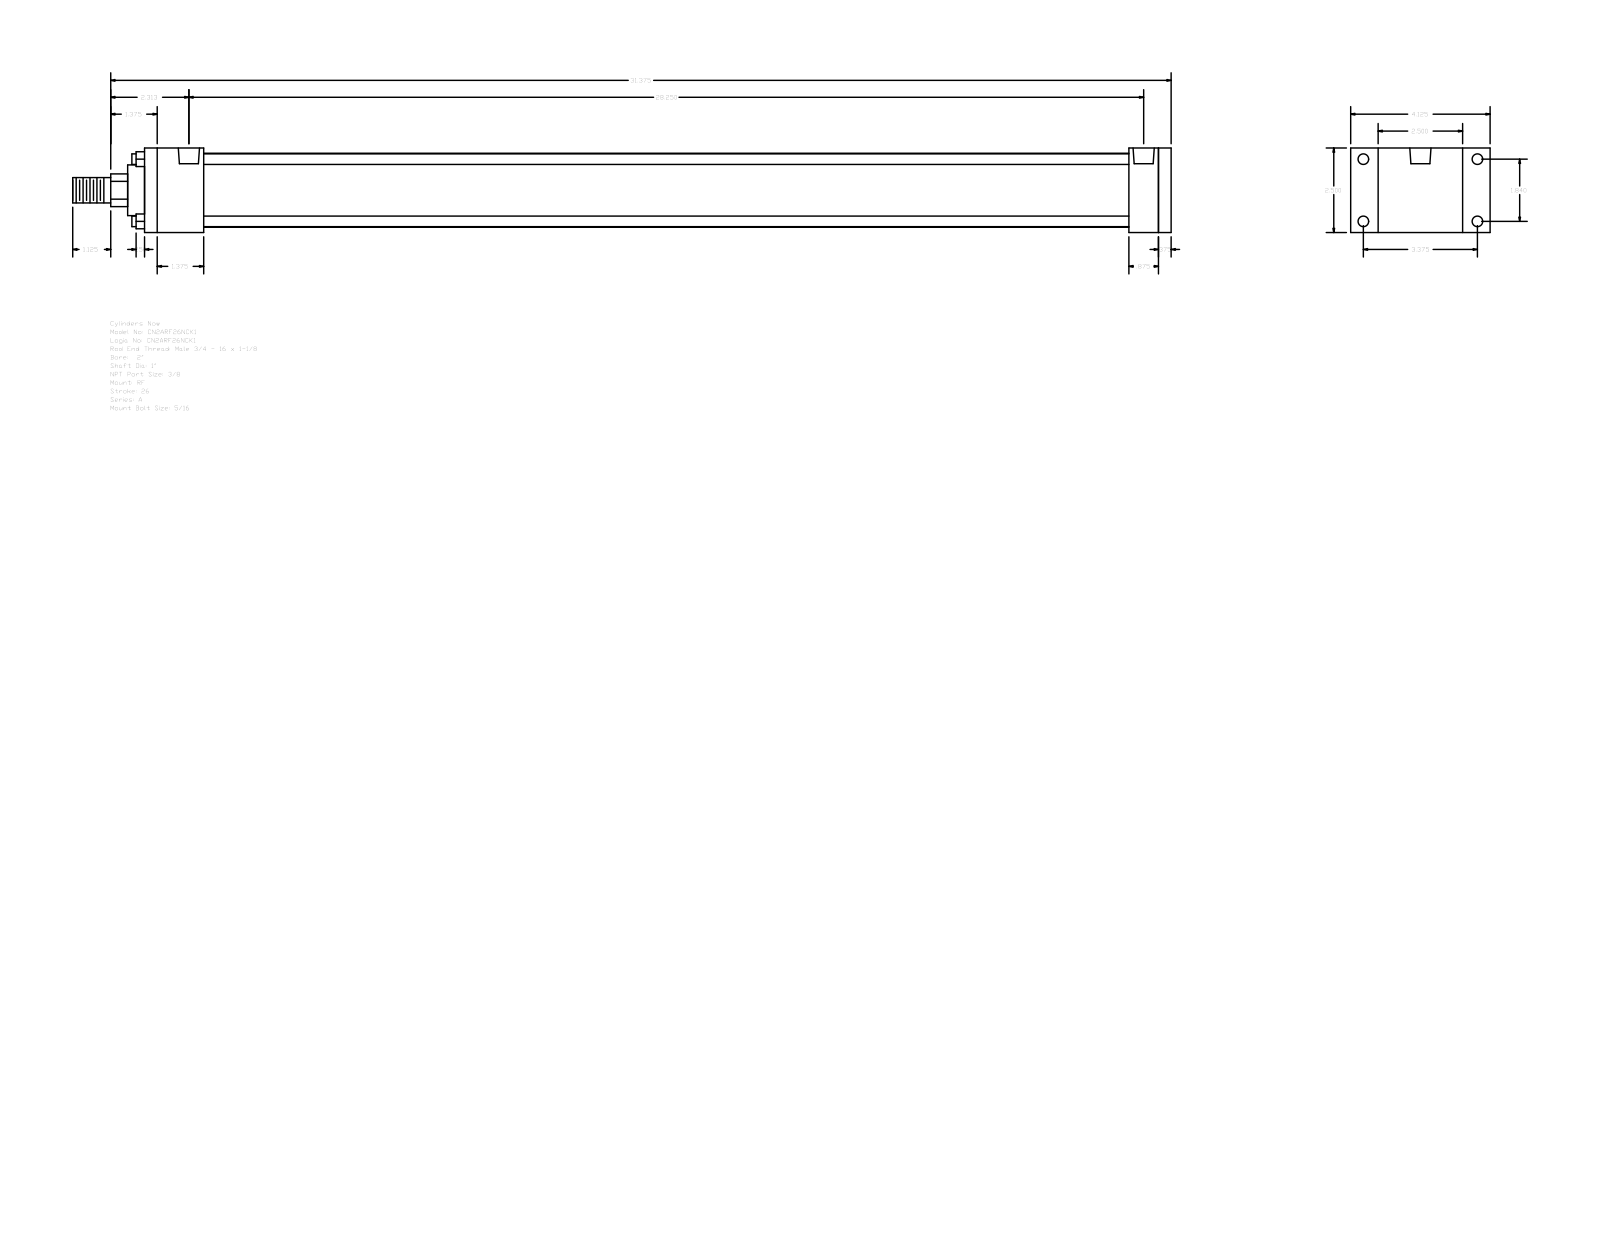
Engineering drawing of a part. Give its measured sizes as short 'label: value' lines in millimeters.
name: A_RF__0200_1
written by: GSSL Pune (CONFIG_CONTROL_DESIGN)
unit: mm
bodies: 0 solids, 92 faces (64 planar, 28 cylindrical, 0 other)
size: 825.5 × 104.78 × 63.5
holes: 4× ⌀5.56, 4× ⌀7.94, 2× ⌀15.93
bosses: 4× ⌀7.94, 1× ⌀55.63, 1× ⌀38.1, 1× ⌀25.4, 1× ⌀19.05
rounds: 1× R12.29
face distances: 63.5, 9.52, 771.52, 762, 44.45, 20.64, 717.55, 727.07, 739.77, 695.32
hole spacings: 46.74, 85.72, 97.63, 711.98, 1.59, 3.98, 713.57, 715.96
